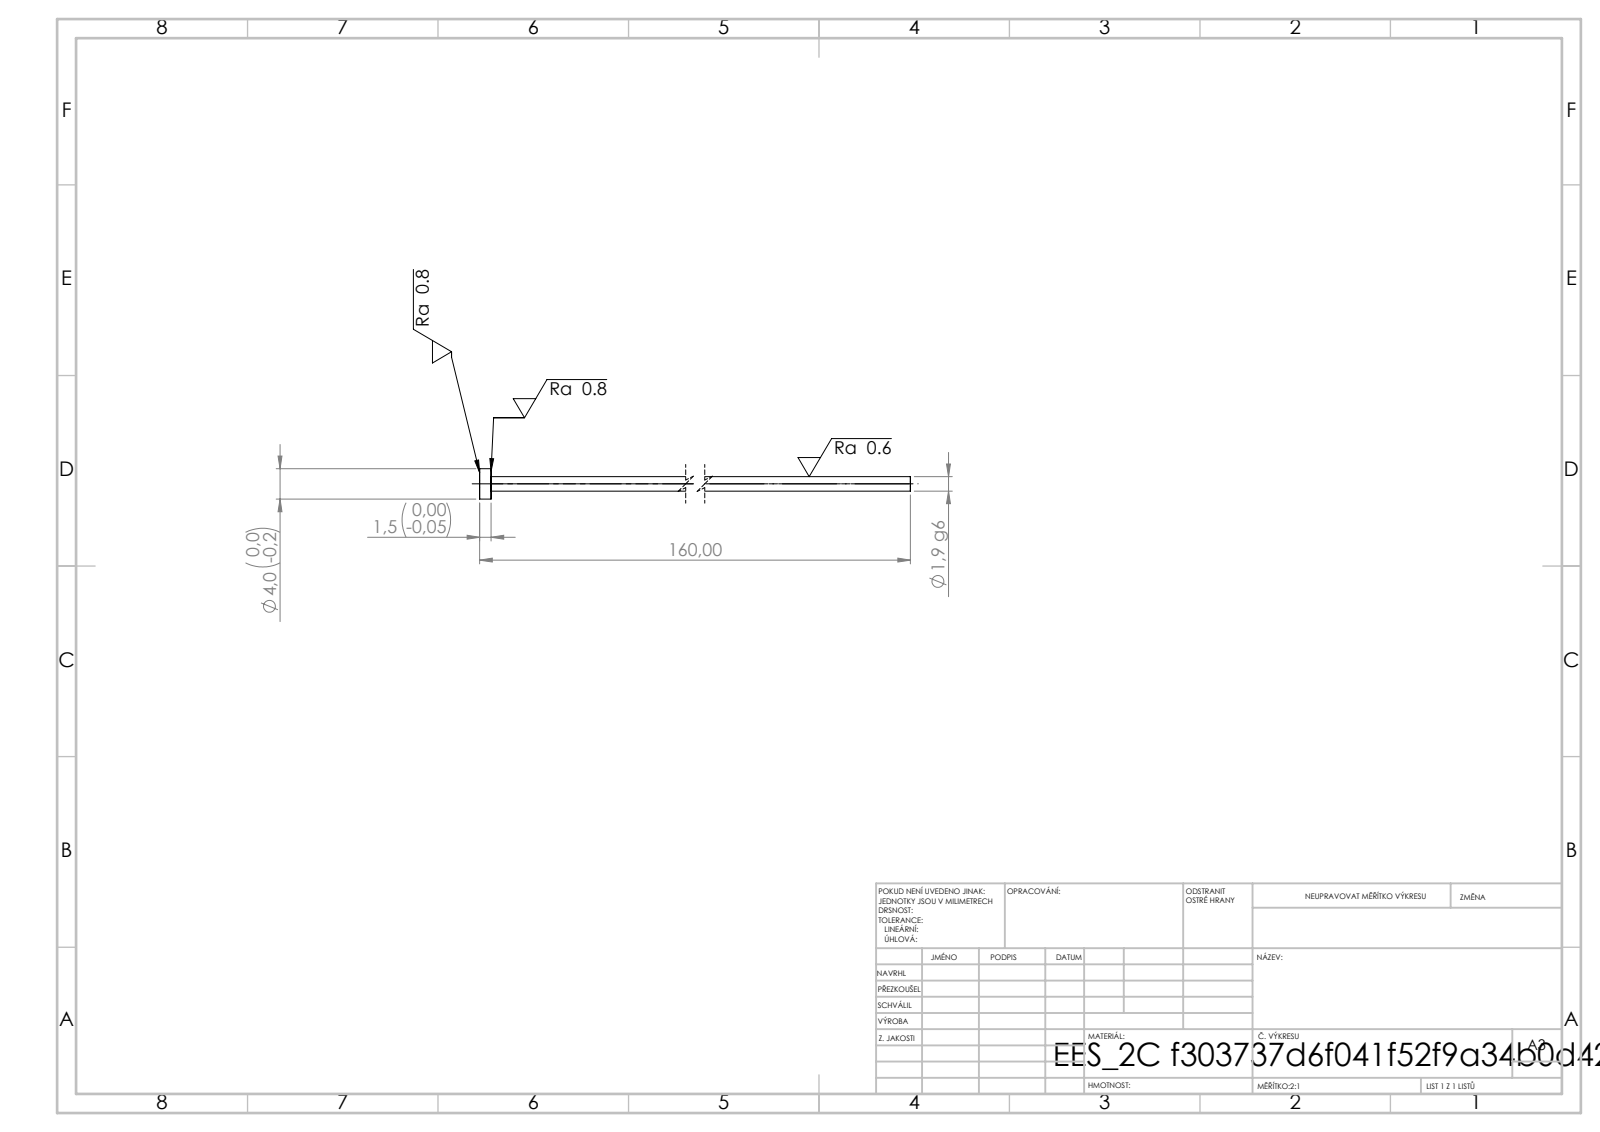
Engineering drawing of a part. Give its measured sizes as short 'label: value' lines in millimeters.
written by: SolidWorks 2019 (CONFIG_CONTROL_DESIGN)
unit: mm
bodies: 1 solid, 7 faces (3 planar, 4 cylindrical, 0 other)
size: 160 × 4 × 4
volume: 468 mm³; area: 990 mm²
bosses: 1× ⌀4, 1× ⌀1.9
face distances: 1.5, 160, 158.5
